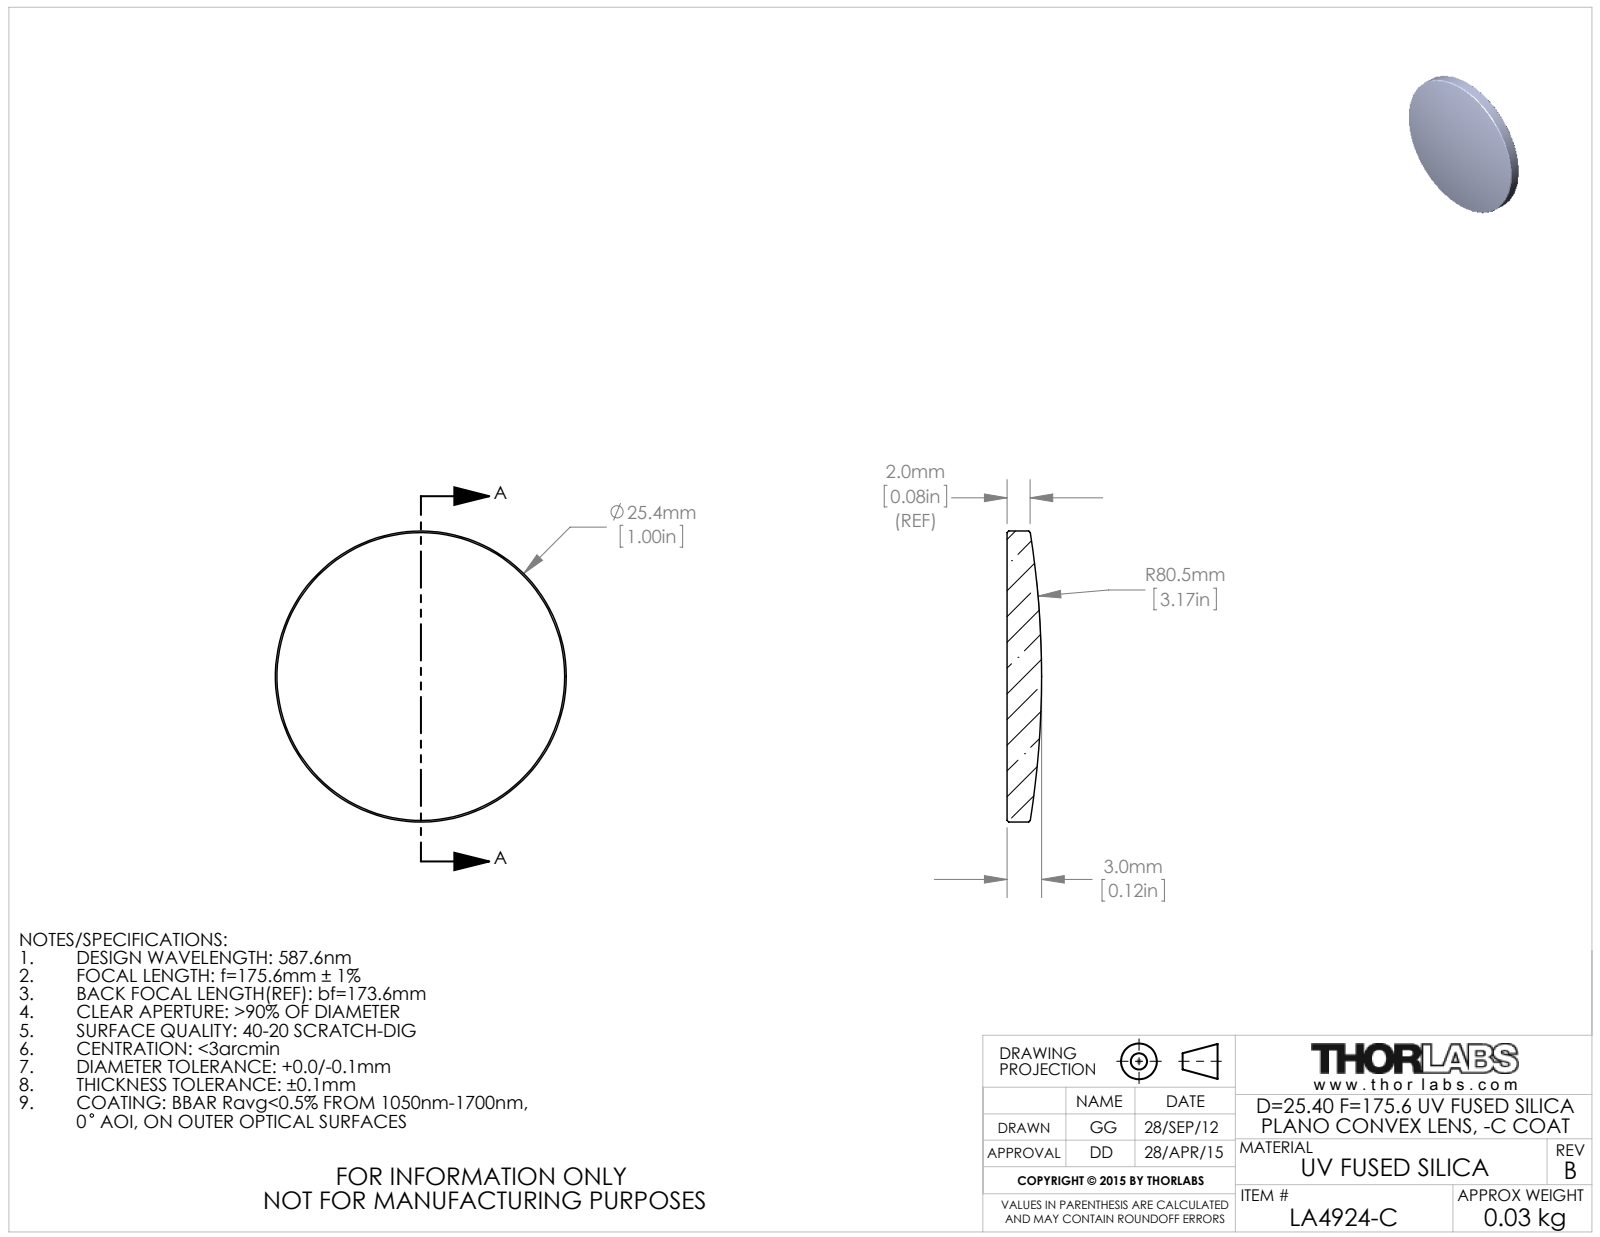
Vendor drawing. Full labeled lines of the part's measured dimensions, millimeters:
Part name (STEP PRODUCT): 25001-E0W
STEP written by: SolidWorks 2014 (CONFIG_CONTROL_DESIGN)
Units: millimetres
Bodies: 1 solid, 9 faces (1 planar, 2 cylindrical, 6 other)
Overall size (bounding box): 25.4 × 25.4 × 3.01
Volume: 1 268 mm³ · Surface area: 1 165 mm²
Round bosses / shafts (diameter × count): ⌀25.4 ×1
